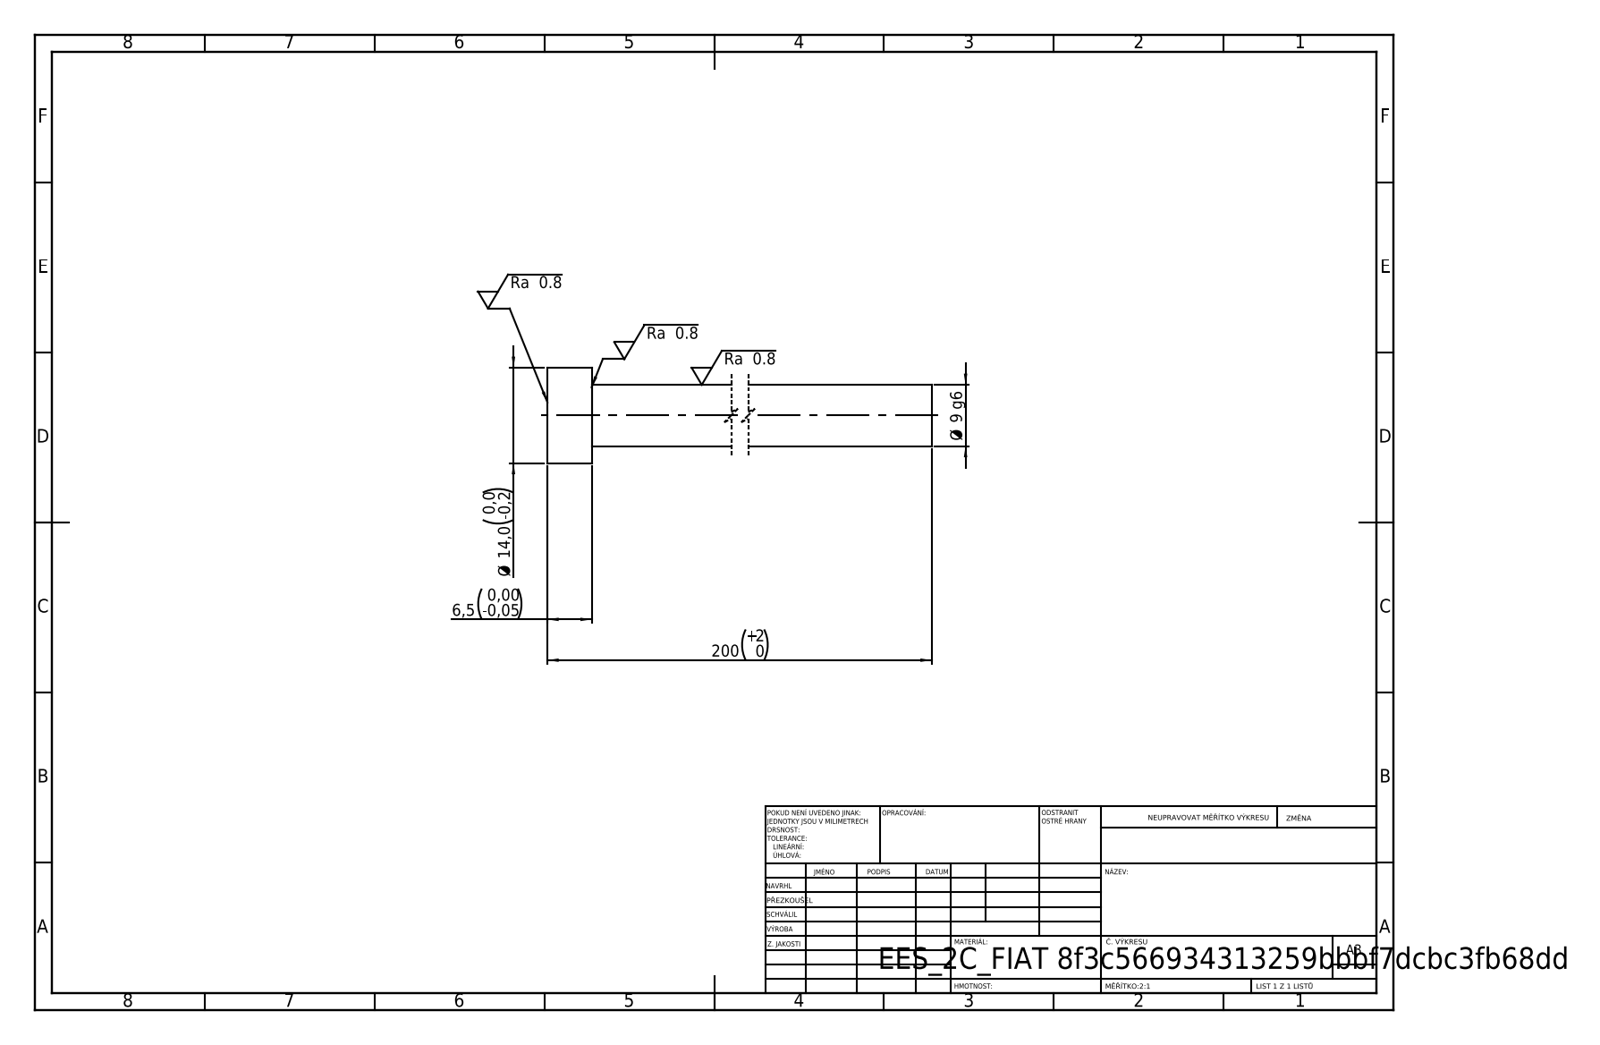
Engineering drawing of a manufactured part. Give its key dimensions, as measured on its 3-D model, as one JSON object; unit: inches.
{"step_written_by": "SolidWorks 2019 (CONFIG_CONTROL_DESIGN)", "units": "inches", "bodies": {"solids": 1, "faces": 7, "planar": 3, "cylindrical": 4, "other": 0}, "overall_size": [7.874, 0.551, 0.551], "volume_in3": 0.812, "surface_area_in2": 9.401, "round_bosses_or_shafts": [[0.551, 1], [0.354, 1]], "face_to_face_distances": [0.256, 7.874, 7.618]}
